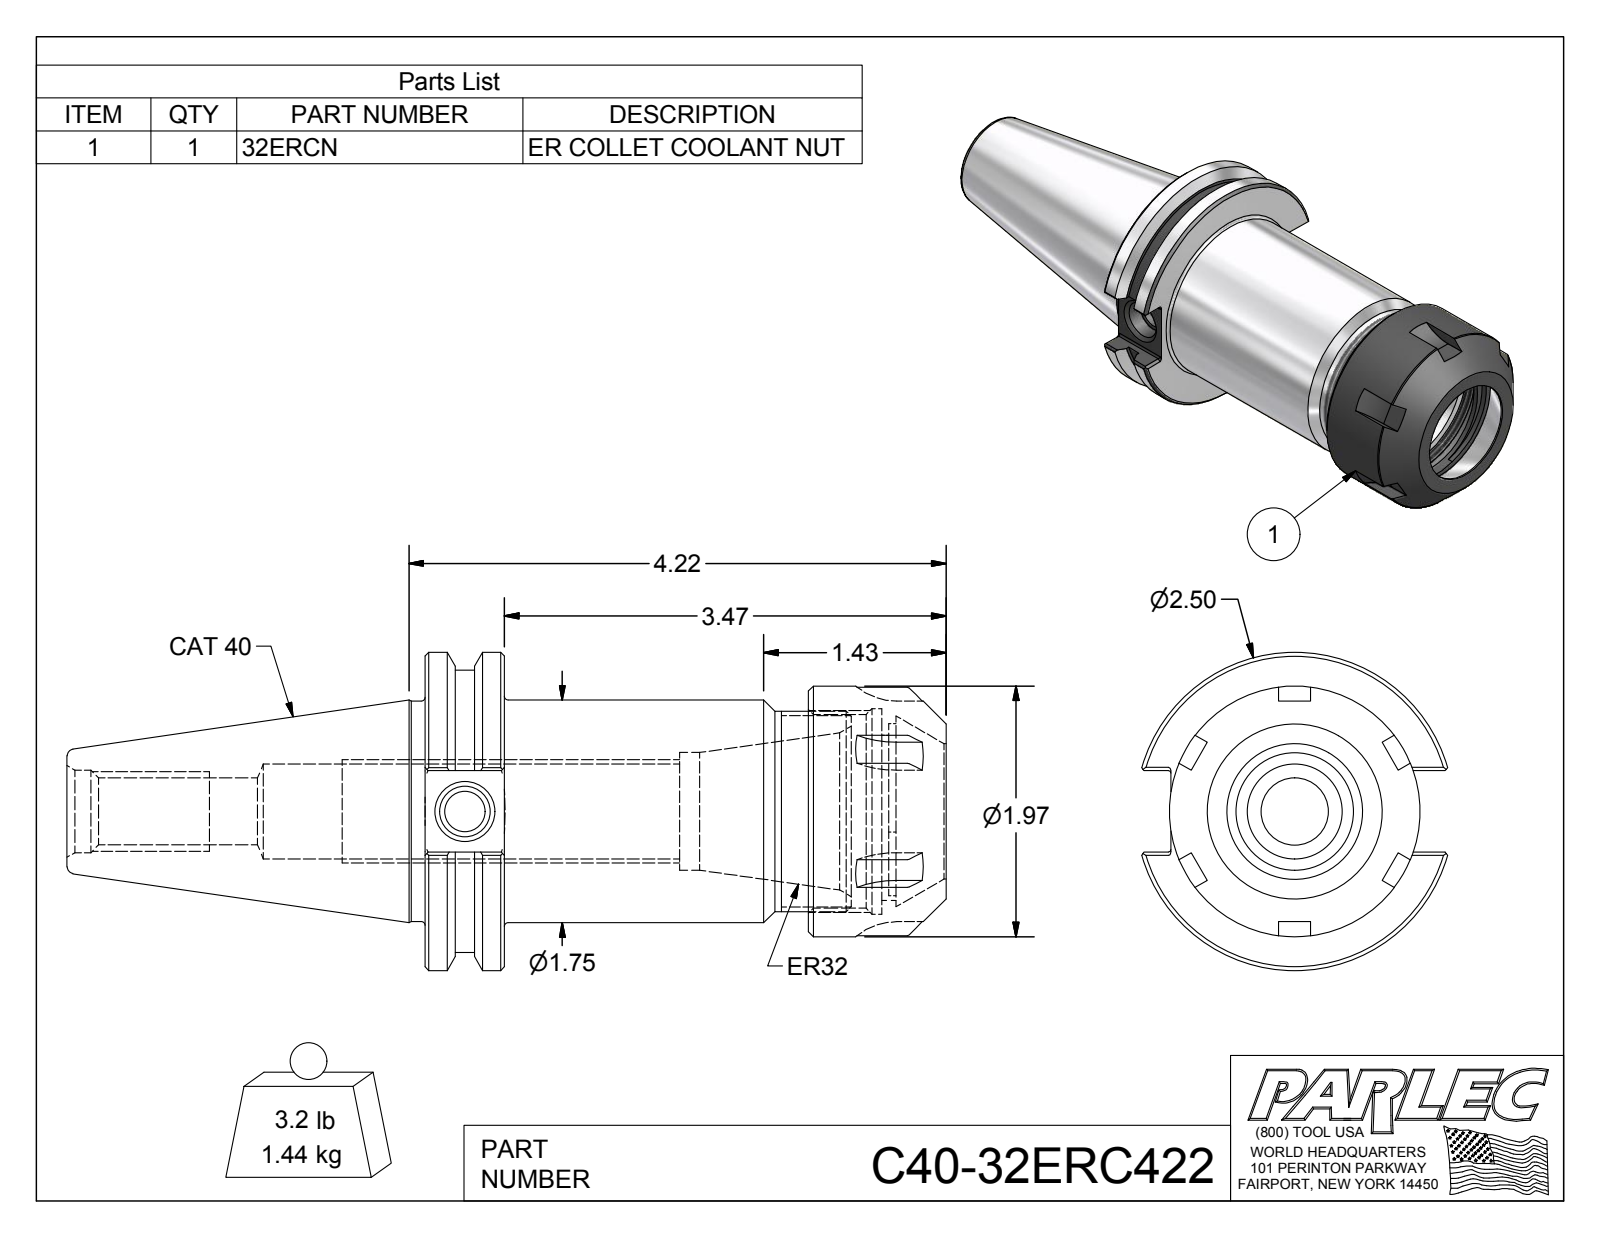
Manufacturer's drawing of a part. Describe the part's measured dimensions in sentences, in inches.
The part is named "C40-32ERC422; C40-32ER4-1; 32ERCN". Its 3-D file was written by "Autodesk Inventor 2012 (AUTOMOTIVE_DESIGN)". It is 2 solids with 127 faces: 55 planar, 39 cylindrical and 33 other. Overall it measures 6.908 by 2.5 by 2.403 inches. Its volume is 11.36 cubic inches and its surface area 69.23 square inches. Round holes: 1 of diameter 0.315, 1 of diameter 0.399, 1 of diameter 0.527, 1 of diameter 0.648, 1 of diameter 0.745, 1 of diameter 0.925, 1 of diameter 1.063, 1 of diameter 1.299, 1 of diameter 1.522, 1 of diameter 1.614. Round bosses or shafts: 1 of diameter 2.5, 1 of diameter 2.219, 1 of diameter 1.969, 1 of diameter 1.75, 1 of diameter 1.73, 1 of diameter 1.575. Partial cylindrical surfaces (rounded edges, fillets, slot ends): 12 of radius 0.02, 6 of radius 0.5, 1 of radius 0.689. The main face-to-face distances are 0.625, 3.012, 2.387, 3.591, 2.966, 0.579, 4.095, 3.47, 1.083, 0.504. The hole center spacings are 0.059.
